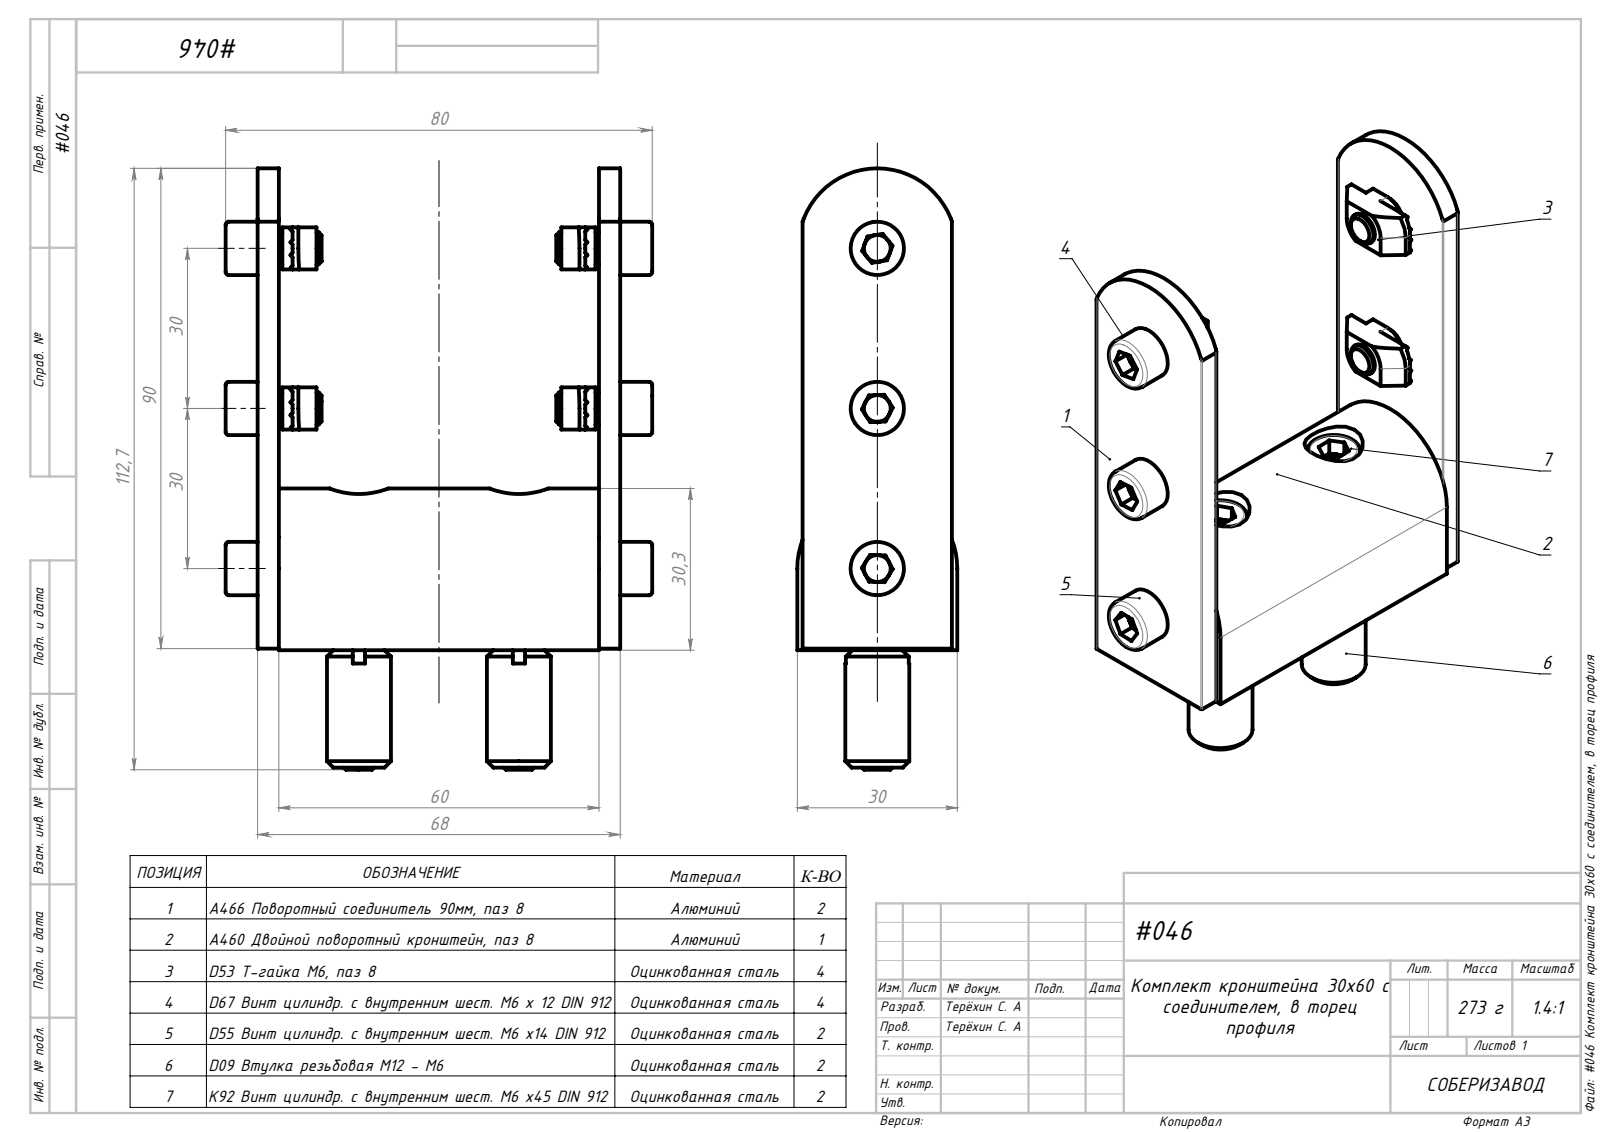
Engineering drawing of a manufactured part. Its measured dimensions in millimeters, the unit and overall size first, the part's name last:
Units: millimetres
Overall size (bounding box): 112.7 × 80 × 30
Round holes (diameter × count): ⌀6.4 ×3, ⌀5 ×2, ⌀5.5 ×2, ⌀6.15 ×2, ⌀11 ×2, ⌀5.15 ×1
Round bosses / shafts (diameter × count): ⌀10 ×5, ⌀6 ×5, ⌀12 ×2
Partial cylindrical surfaces — rounded edges, fillets, slot ends (radius × count): R0.2 ×8, R4 ×8, R6.87 ×4, R14.8 ×1, R15 ×1
Main face-to-face distances: 4, 64, 60, 68, 30, 1, 29, 28, 6, 22.3
Hole centre spacings: 30, 60
Volume: 77 011 mm³ · Surface area: 32 475 mm²
Bodies: 17 solids, 504 faces (283 planar, 101 cylindrical, 120 other)
Part name (STEP PRODUCT): K92 Винт цилиндр. с внутренним шест. М6 х45 DIN 912; #046 Комплект кронштейна 30х60 с соединителем, в торец профиля; D09 Втулка резьбовая М12 - М6 _00; D67 Винт цилиндр. с внутренним шест. М6 х 12 DIN 912 (+4 more)
STEP written by: SolidWorks 2021 (AUTOMOTIVE_DESIGN)
